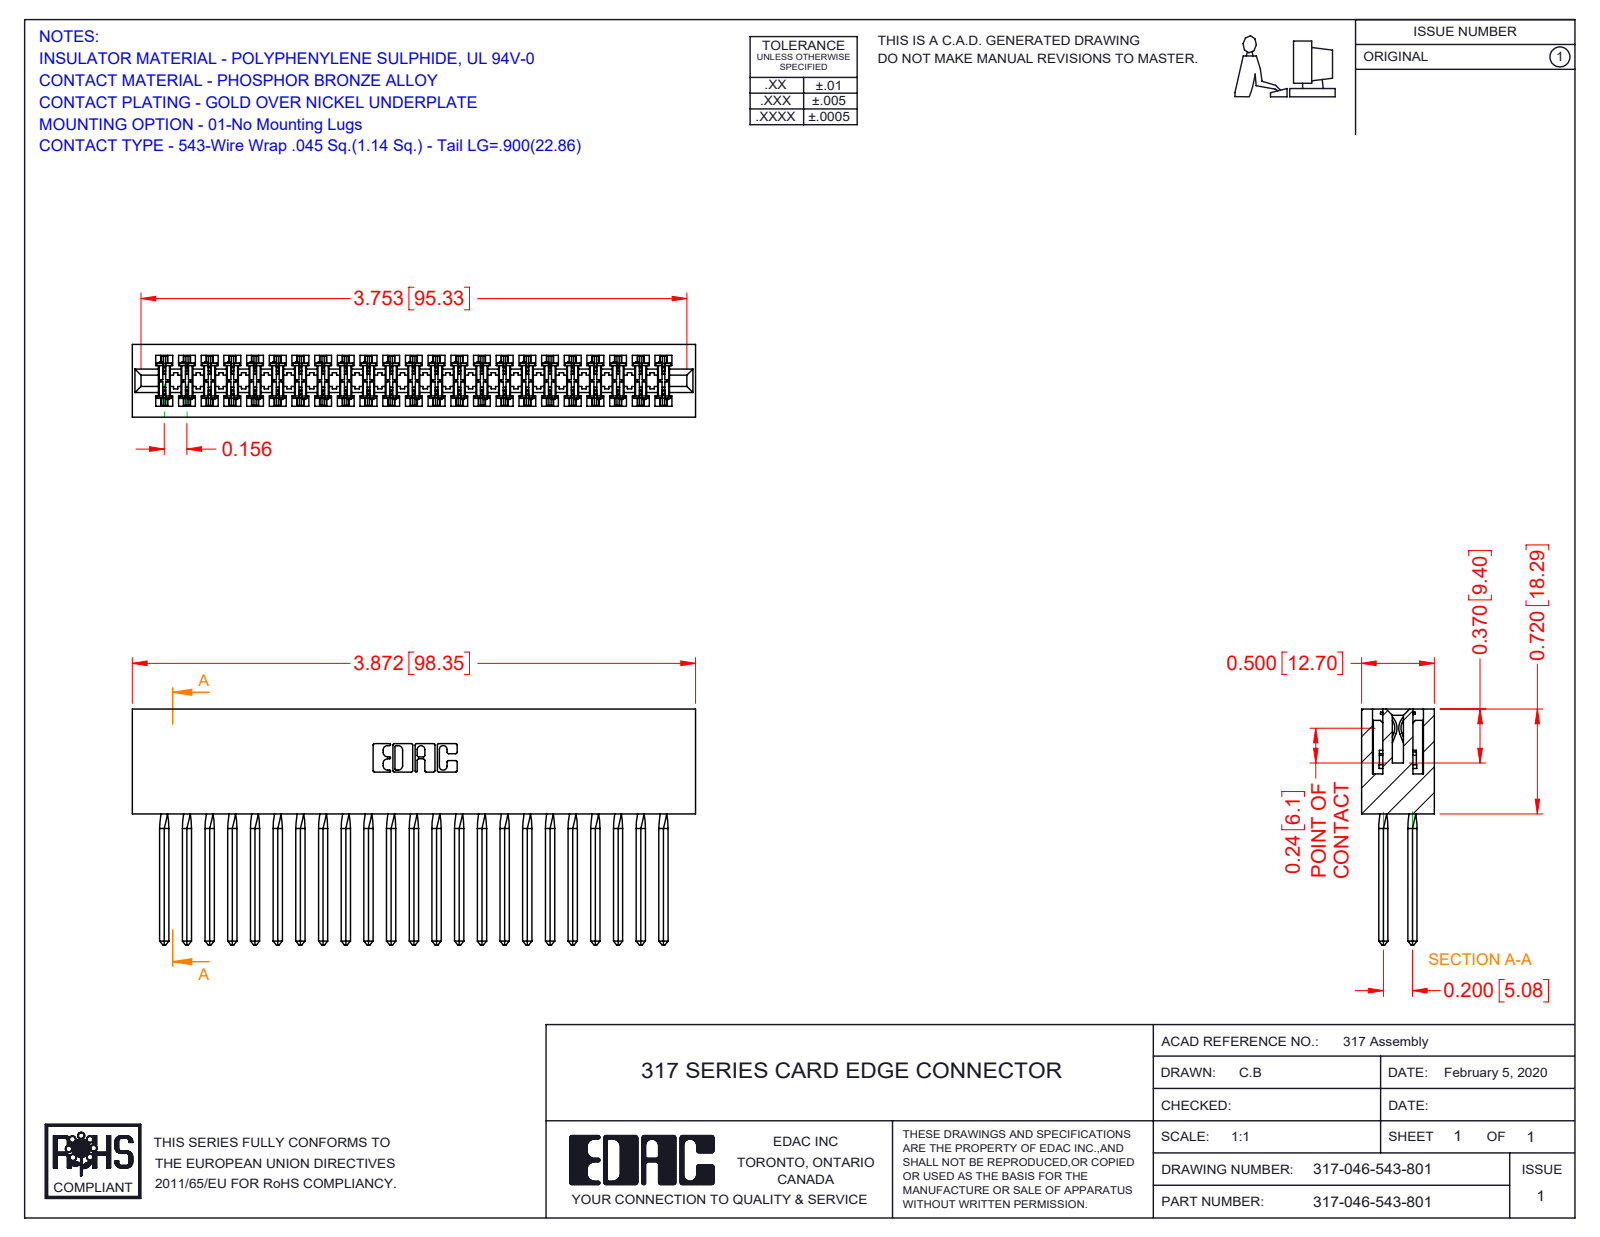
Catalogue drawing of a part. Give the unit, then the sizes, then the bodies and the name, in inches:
Units: inches
Overall size (bounding box): 3.872 × 1.62 × 0.5
Partial cylindrical surfaces — rounded edges, fillets, slot ends (radius × count): R0.015 ×92, R0.01 ×22, R0.007 ×6, R0.031 ×6, R0.026 ×3, R0.095 ×2, R0.1 ×2, R0.11 ×2
Main face-to-face distances: 0.5, 0.075, 0.425, 0.11, 0.35, 0.195, 0.22, 0.094, 0.72, 0.116
Volume: 1.091 in³ · Surface area: 41.33 in²
Bodies: 47 solids, 4184 faces (3408 planar, 592 cylindrical, 184 other)
Part name (STEP PRODUCT): 317-290-001_543; 317 Part_Lugless; 317-046-543-801
STEP written by: SolidWorks 2016 (CONFIG_CONTROL_DESIGN)
